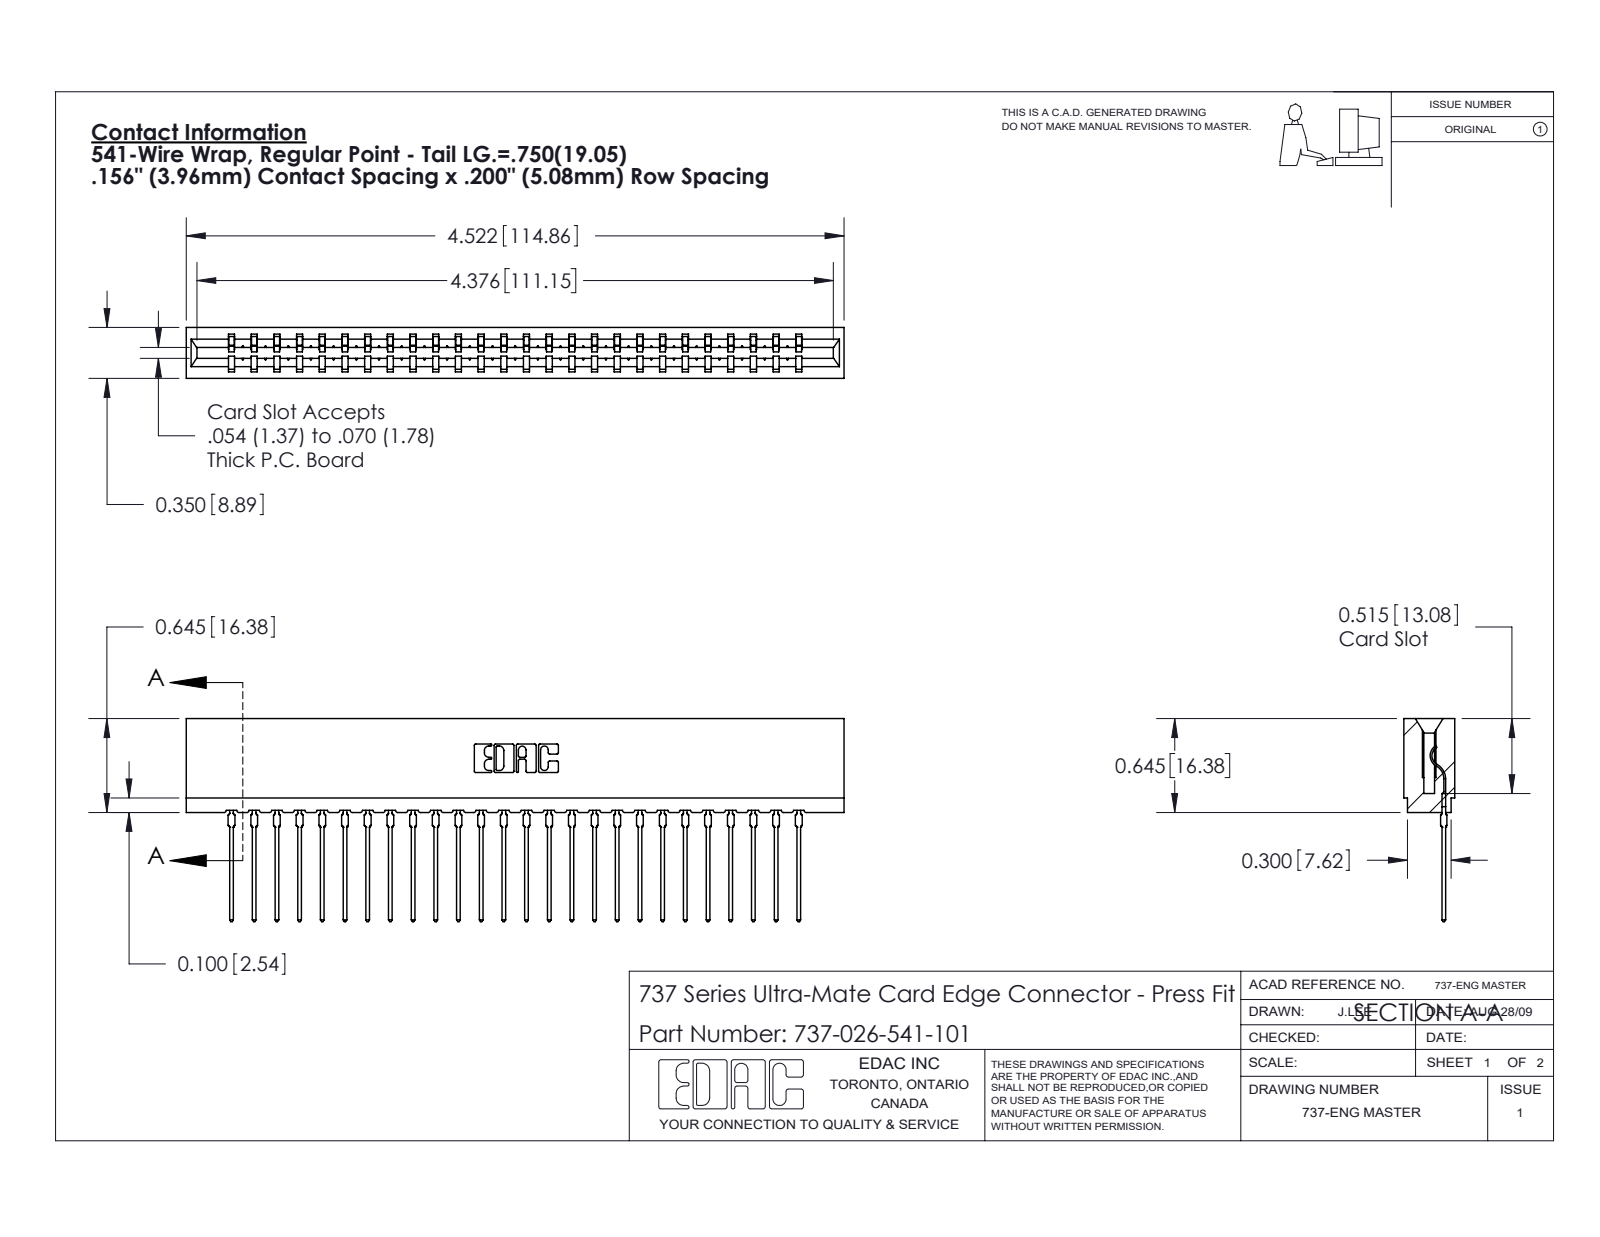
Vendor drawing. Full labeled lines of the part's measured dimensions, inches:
Part name (STEP PRODUCT): 745-292-001_541; 737-026-541-101; 737 Part_Insulator Option - 01
STEP written by: SolidWorks 2020 (CONFIG_CONTROL_DESIGN)
Units: inches
Bodies: 27 solids, 3032 faces (1822 planar, 534 cylindrical, 676 other)
Overall size (bounding box): 4.522 × 1.396 × 0.35
Volume: 0.691 in³ · Surface area: 24 in²
Partial cylindrical surfaces — rounded edges, fillets, slot ends (radius × count): R0.015 ×52, R0.021 ×52, R0.01 ×22, R0.007 ×6, R0.031 ×6, R0.005 ×4, R0.011 ×4, R0.026 ×3
Main face-to-face distances: 0.138, 0.212, 0.35, 0.156, 0.074, 0.624, 0.468, 0.78, 0.063, 0.287
